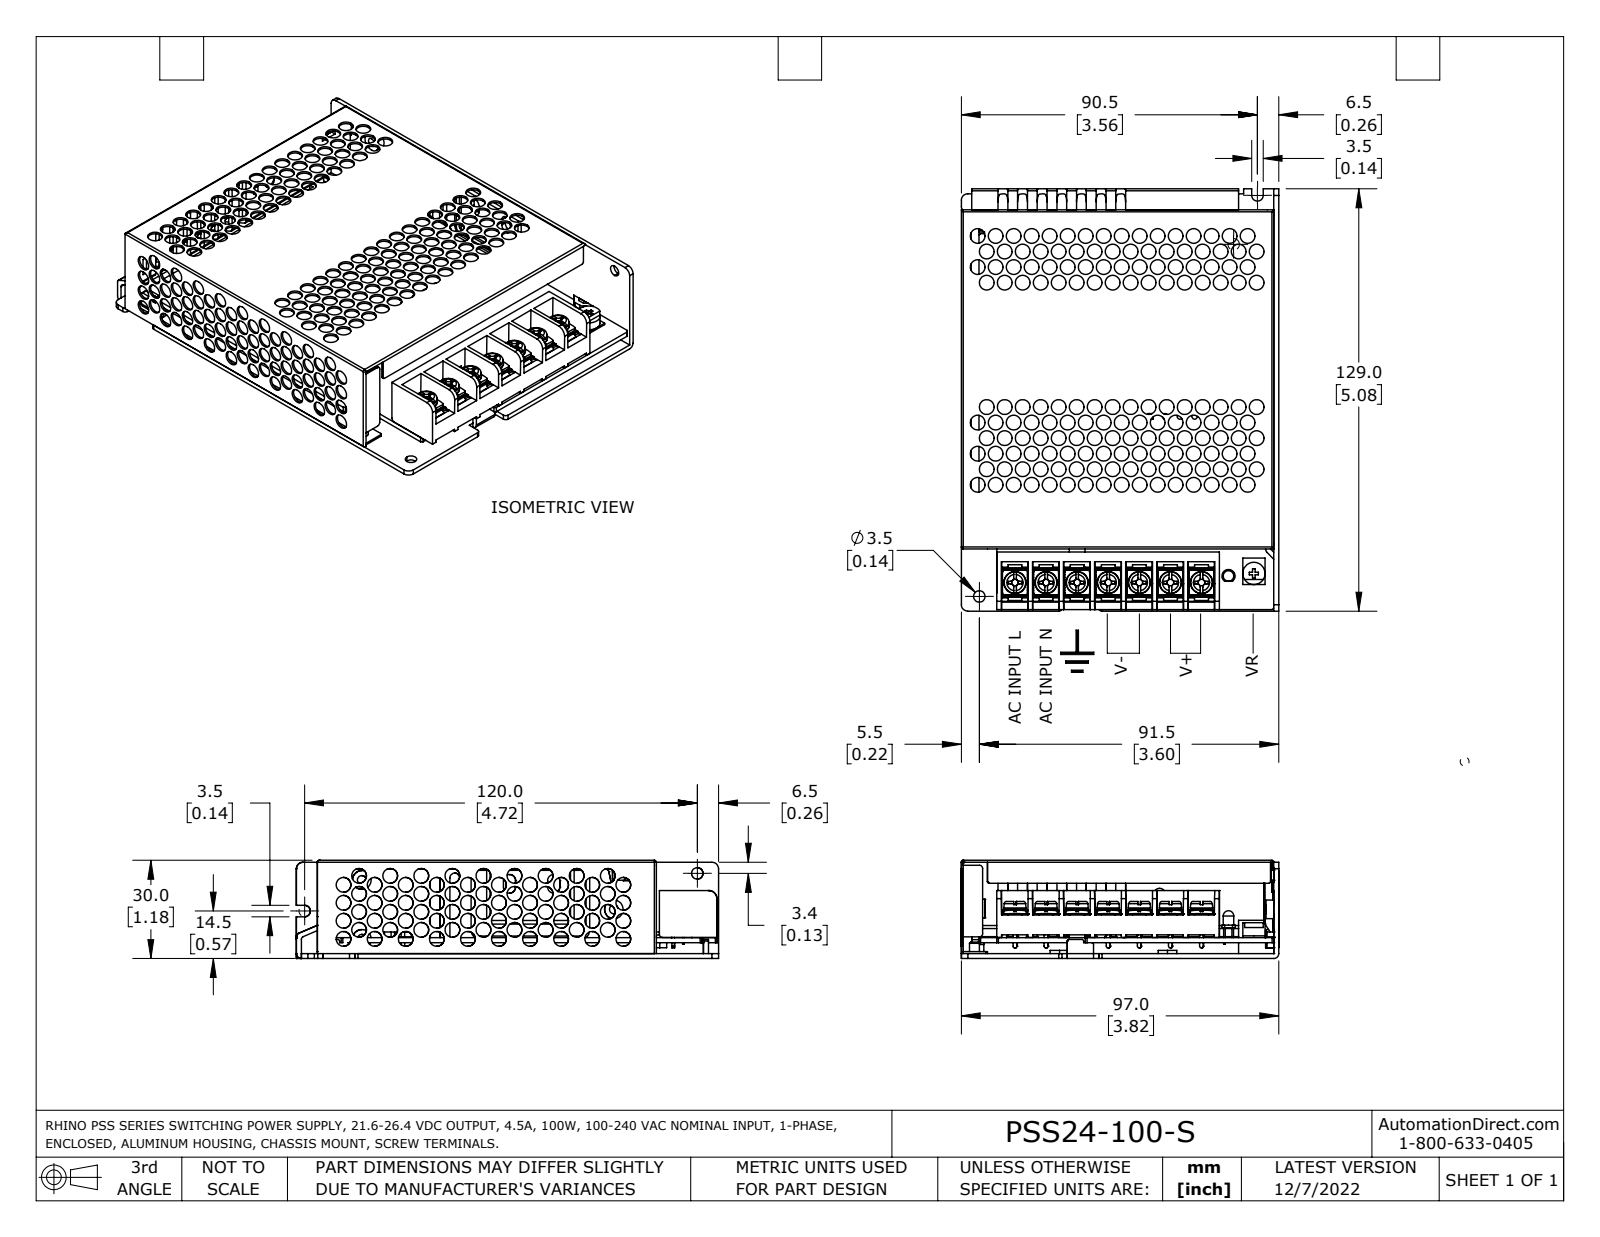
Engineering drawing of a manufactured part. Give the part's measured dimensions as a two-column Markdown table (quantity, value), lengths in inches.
| quantity | value |
| --- | --- |
| part name | PSS12-100-S |
| STEP written by | SolidWorks 2021 (AUTOMOTIVE_DESIGN) |
| units | inches |
| bodies | 2 solids, 2150 faces (1225 planar, 549 cylindrical, 376 other) |
| overall size | 5.079 × 3.819 × 1.181 |
| volume | 3.658 in³ |
| surface area | 144.3 in² |
| round holes (diameter × count) | 0.177 × 236, 0.138 × 10, 0.126 × 7, 0.106 × 5, 0.067 × 3, 0.039 × 1, 0.047 × 1, 0.118 × 1 |
| round bosses / shafts (diameter × count) | 0.125 × 6, 0.224 × 5, 0.02 × 2, 0.268 × 1, 0.236 × 1, 0.217 × 1, 0.157 × 1, 0.126 × 1 |
| partial cylindrical surfaces (radius × count) | 0.039 × 45, 0.016 × 40, 0.02 × 34, 0.059 × 31, 0.024 × 11, 0.079 × 8, 0.012 × 4, 0.073 × 4 |
| main face-to-face distances | 0.059, 0.252, 0.193, 0.189, 0.024, 0.13, 0.063, 1.122, 1.098, 0.906 |
| hole center spacings | 0.432, 0.374, 0.217, 0.572, 0.216, 0.779, 0.571, 0.748 |
